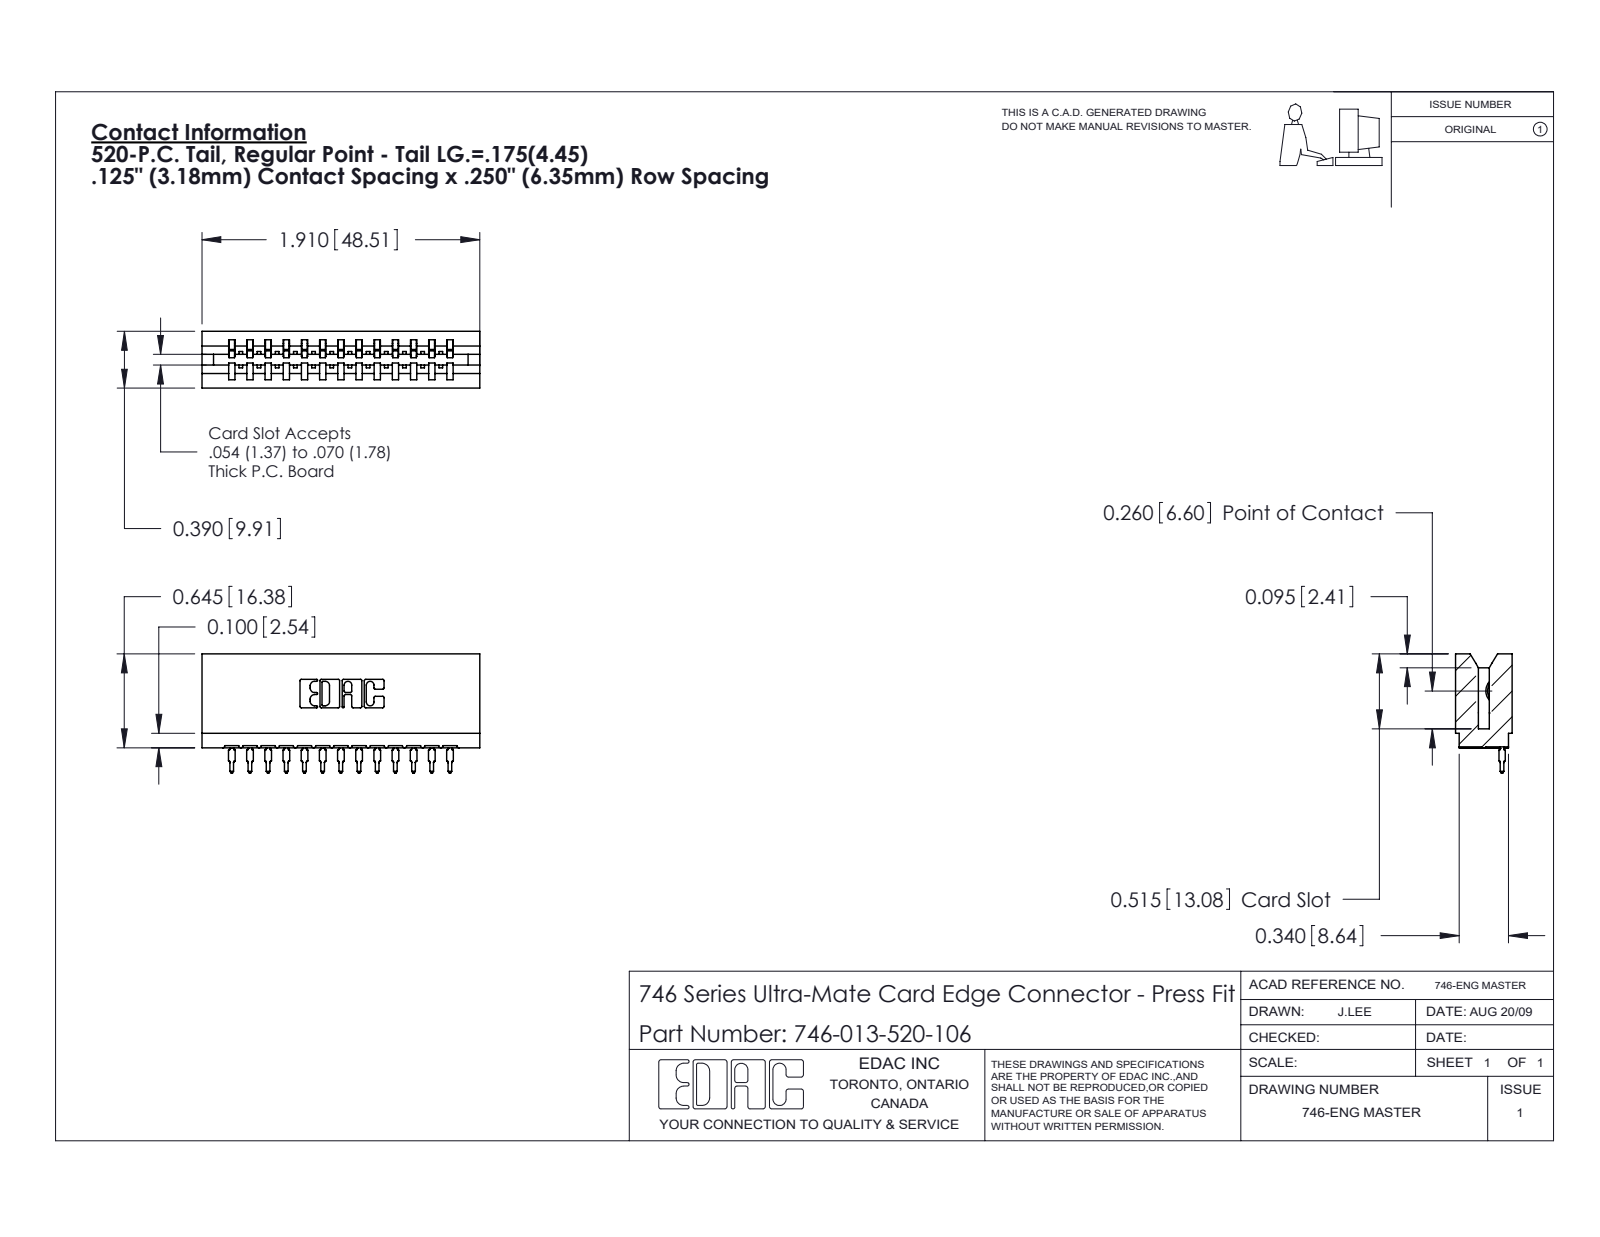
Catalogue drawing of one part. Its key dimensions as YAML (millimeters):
part_name: "746-292-001_520; 746-013-520-106; 746 Part_.515 Slot Depth - 06"
step_written_by: "SolidWorks 2020 (CONFIG_CONTROL_DESIGN)"
units: millimeters
bodies: {solids: 14, faces: 1502, planar: 875, cylindrical: 289, other: 338}
overall_size: [48.5, 20.8, 9.9]
volume: 5230
surface_area: 7181
partial_cylinders:
  - {radius: 0.5, count: 26}
  - {radius: 0.3, count: 22}
  - {radius: 0.4, count: 14}
  - {radius: 0.2, count: 6}
  - {radius: 0.8, count: 6}
  - {radius: 0.1, count: 4}
  - {radius: 0.3, count: 4}
  - {radius: 0.7, count: 3}
face_to_face_distances: [6.4, 8.5, 1.4, 12.7, 9.9, 3.2, 3.2, 7.4, 19.1, 1.1]
